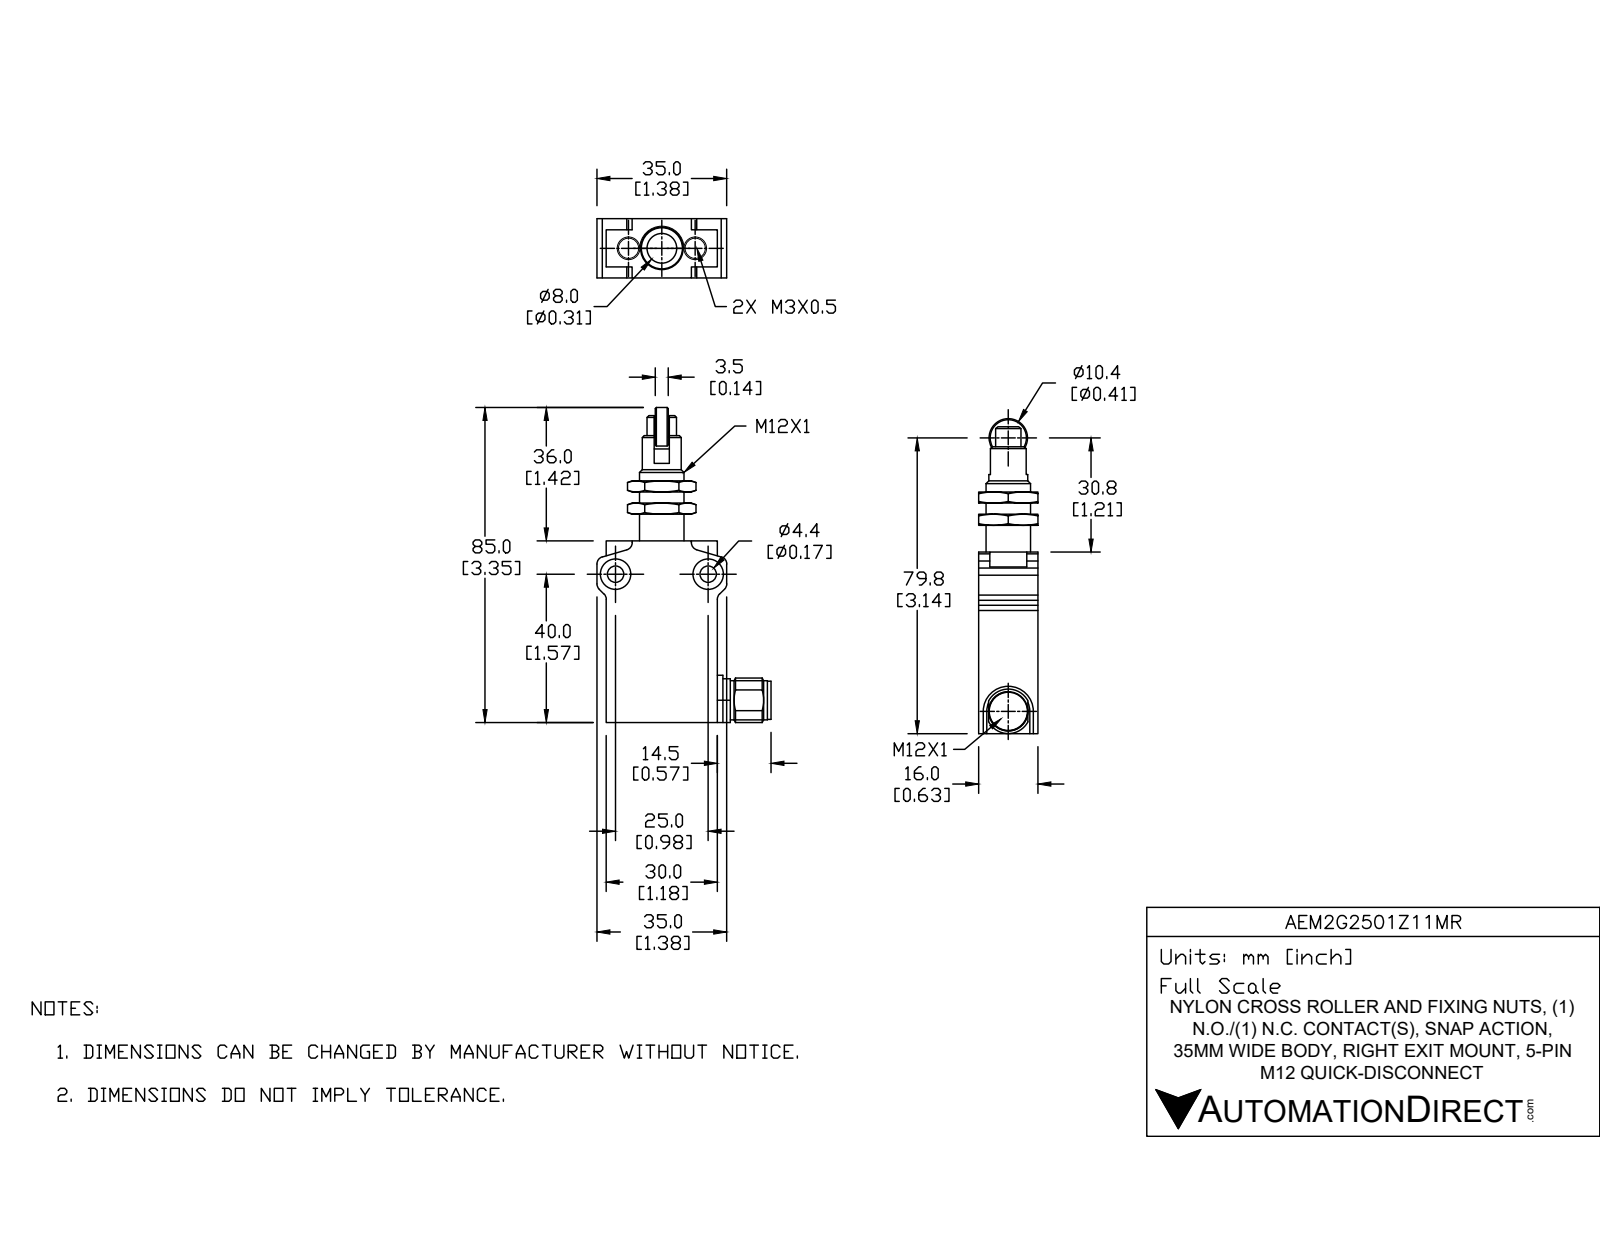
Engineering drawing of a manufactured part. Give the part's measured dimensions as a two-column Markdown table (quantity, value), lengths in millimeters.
| quantity | value |
| --- | --- |
| part name | em2g2501MR; EM2MDX; SCATOLA EM2; CONNETTORE EM2 (+1 more) |
| STEP written by | Autodesk Inventor 2019 (AUTOMOTIVE_DESIGN) |
| units | millimeters |
| bodies | 6 solids, 199 faces (83 planar, 53 cylindrical, 63 other) |
| overall size | 88 × 46.5 × 18.48 |
| volume | 27 418 mm³ |
| surface area | 11 864 mm² |
| round holes (diameter × count) | 3 × 2, 4.4 × 2, 8.2 × 2, 8.05 × 1, 12 × 1 |
| round bosses / shafts (diameter × count) | 12 × 1, 10.6 × 1, 10.5 × 1, 10.4 × 1, 10.3 × 1, 7.95 × 1, 5.6 × 1 |
| partial cylindrical surfaces (radius × count) | 2 × 8, 6.5 × 1 |
| main face-to-face distances | 16, 30, 12, 3, 6, 52, 47.2, 4.8, 9, 4 |
| hole center spacings | 9.5, 19, 25 |
